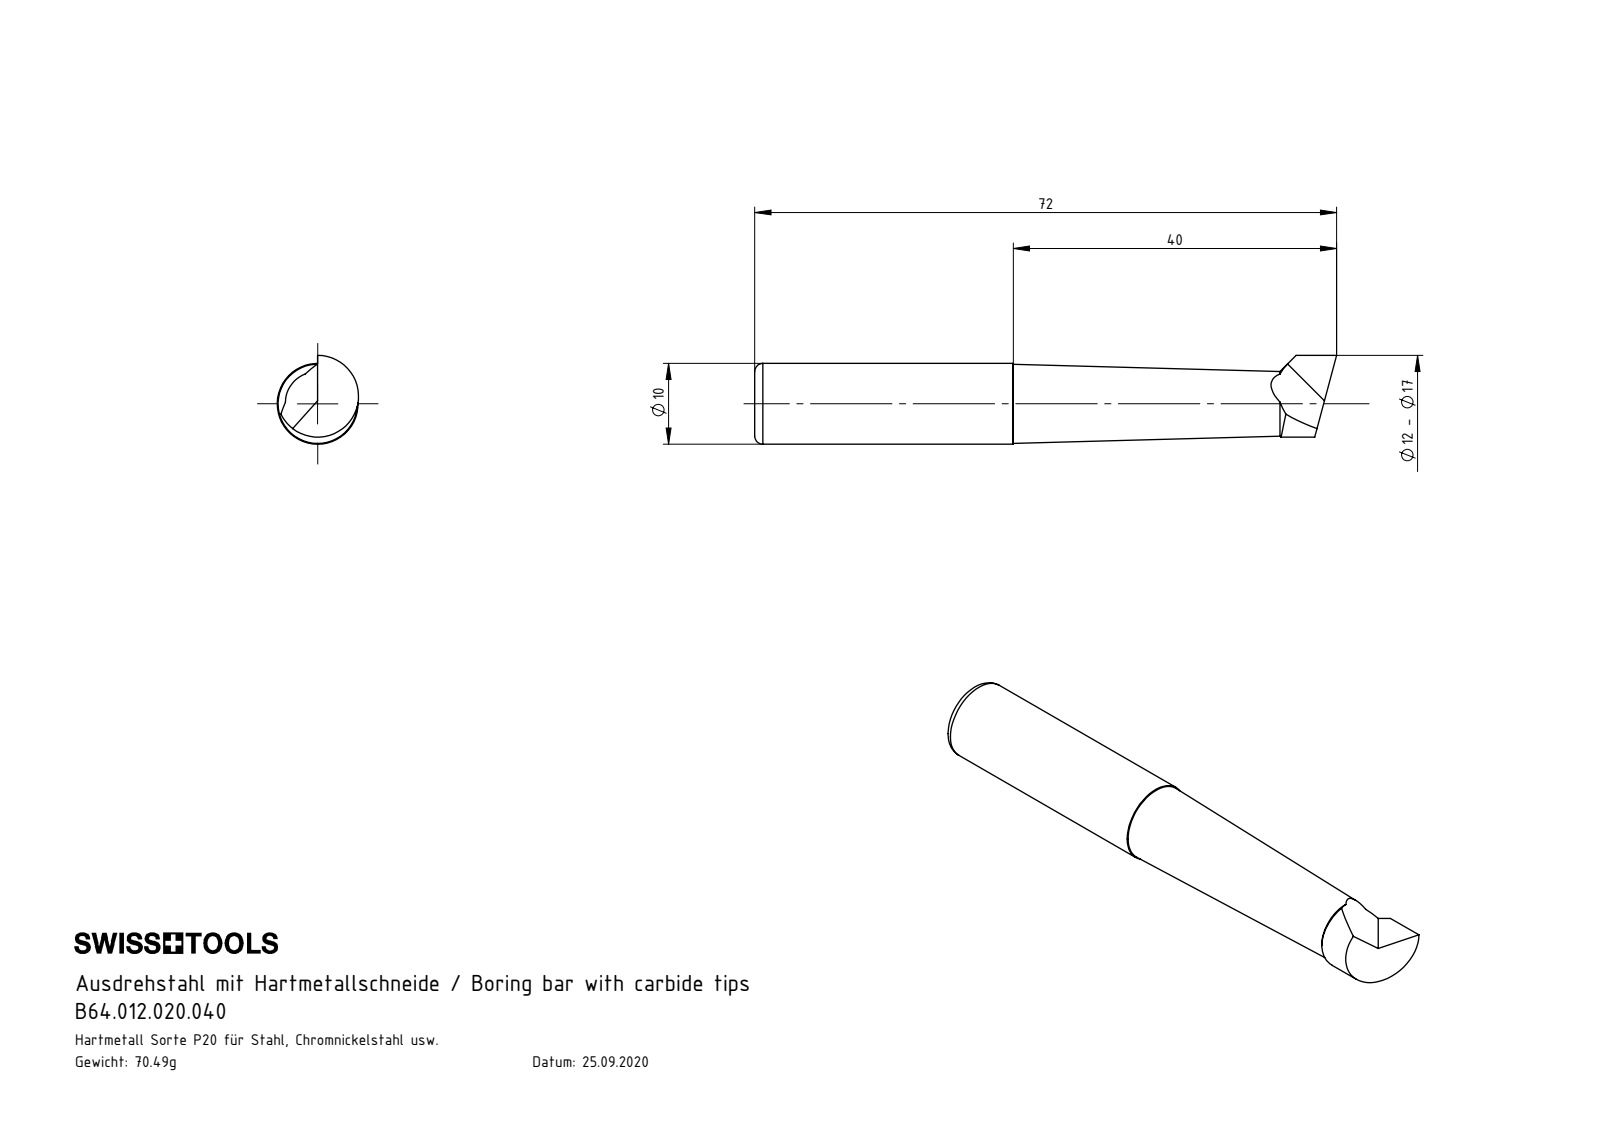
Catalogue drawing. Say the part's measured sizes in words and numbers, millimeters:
The part is named "B64.012.020.040". Its 3-D file was written by "SolidWorks 2022 (CONFIG_CONTROL_DESIGN)". It is 1 solid with 16 faces: 4 planar, 3 cylindrical and 9 other. Overall it measures 72 by 11 by 10.06 millimeters. Its volume is 4 862 cubic millimeters and its surface area 2 217 square millimeters. Round bosses or shafts: 1 of diameter 10. Partial cylindrical surfaces (rounded edges, fillets, slot ends): 1 of radius 5.06.
